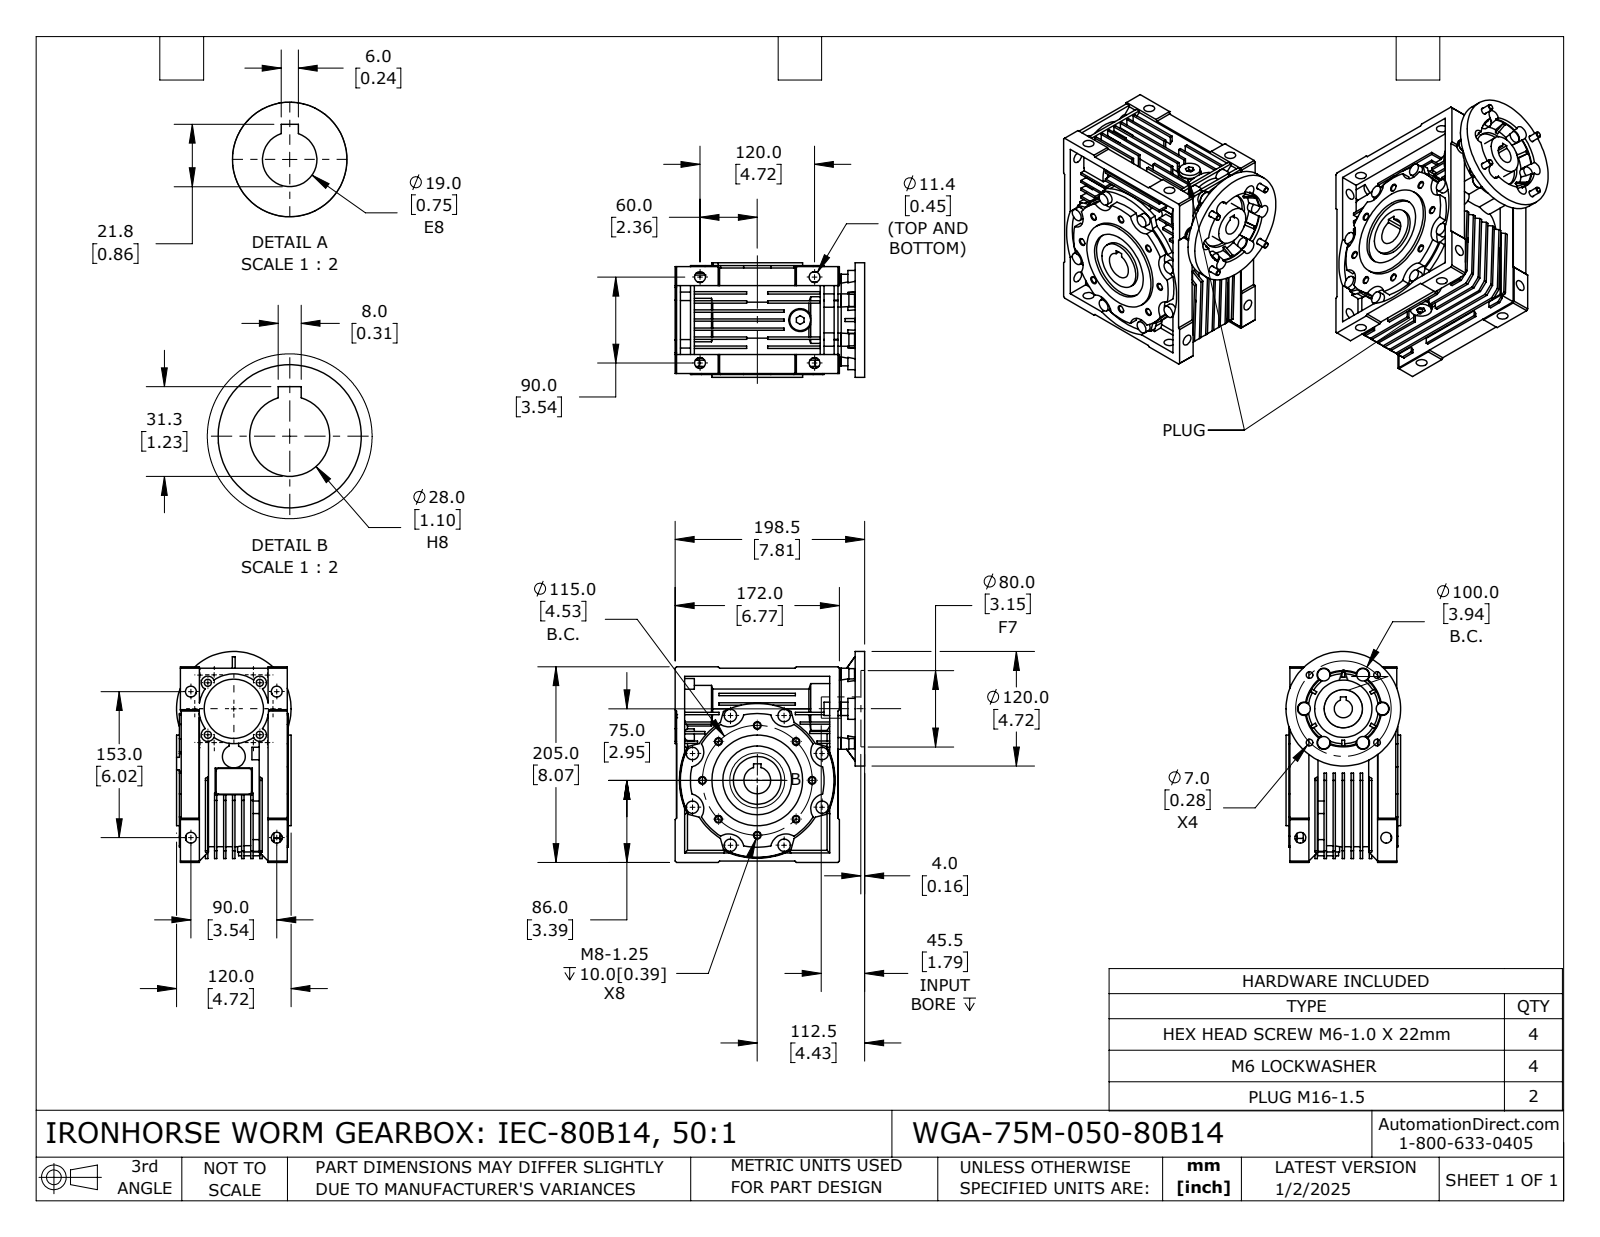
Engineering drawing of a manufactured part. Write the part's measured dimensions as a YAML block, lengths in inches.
part_name: "WGA-75M-050-80B14"
step_written_by: "SolidWorks 2024 (CONFIG_CONTROL_DESIGN)"
units: inches
bodies: {solids: 16, faces: 1304, planar: 703, cylindrical: 433, other: 168}
overall_size: [8.701, 8.228, 4.724]
volume: 174.1
surface_area: 745.4
round_holes:
  - {diameter: 0.262, count: 8}
  - {diameter: 0.448, count: 8}
  - {diameter: 0.24, count: 4}
  - {diameter: 0.276, count: 4}
  - {diameter: 0.293, count: 4}
  - {diameter: 0.571, count: 2}
  - {diameter: 0.748, count: 1}
  - {diameter: 0.787, count: 1}
  - {diameter: 1.102, count: 1}
  - {diameter: 1.535, count: 1}
  - {diameter: 1.654, count: 1}
  - {diameter: 1.969, count: 1}
round_bosses_or_shafts:
  - {diameter: 0.512, count: 14}
  - {diameter: 0.48, count: 4}
  - {diameter: 0.236, count: 4}
  - {diameter: 0.945, count: 3}
  - {diameter: 0.866, count: 2}
  - {diameter: 0.622, count: 2}
  - {diameter: 0.539, count: 2}
  - {diameter: 5.509, count: 1}
partial_cylinders:
  - {radius: 0.276, count: 10}
  - {radius: 0.63, count: 8}
  - {radius: 0.433, count: 6}
  - {radius: 0.098, count: 4}
  - {radius: 1.417, count: 1}
  - {radius: 1.437, count: 1}
  - {radius: 1.535, count: 1}
  - {radius: 1.575, count: 1}
face_to_face_distances: [0.374, 0.098, 0.748, 0.472, 0.394, 0.276, 0.65, 1.122, 1.093, 0.846]
hole_center_spacings: [1.733, 2.264, 2.485, 3.202, 4.183, 0.453, 1.515, 1.969]
